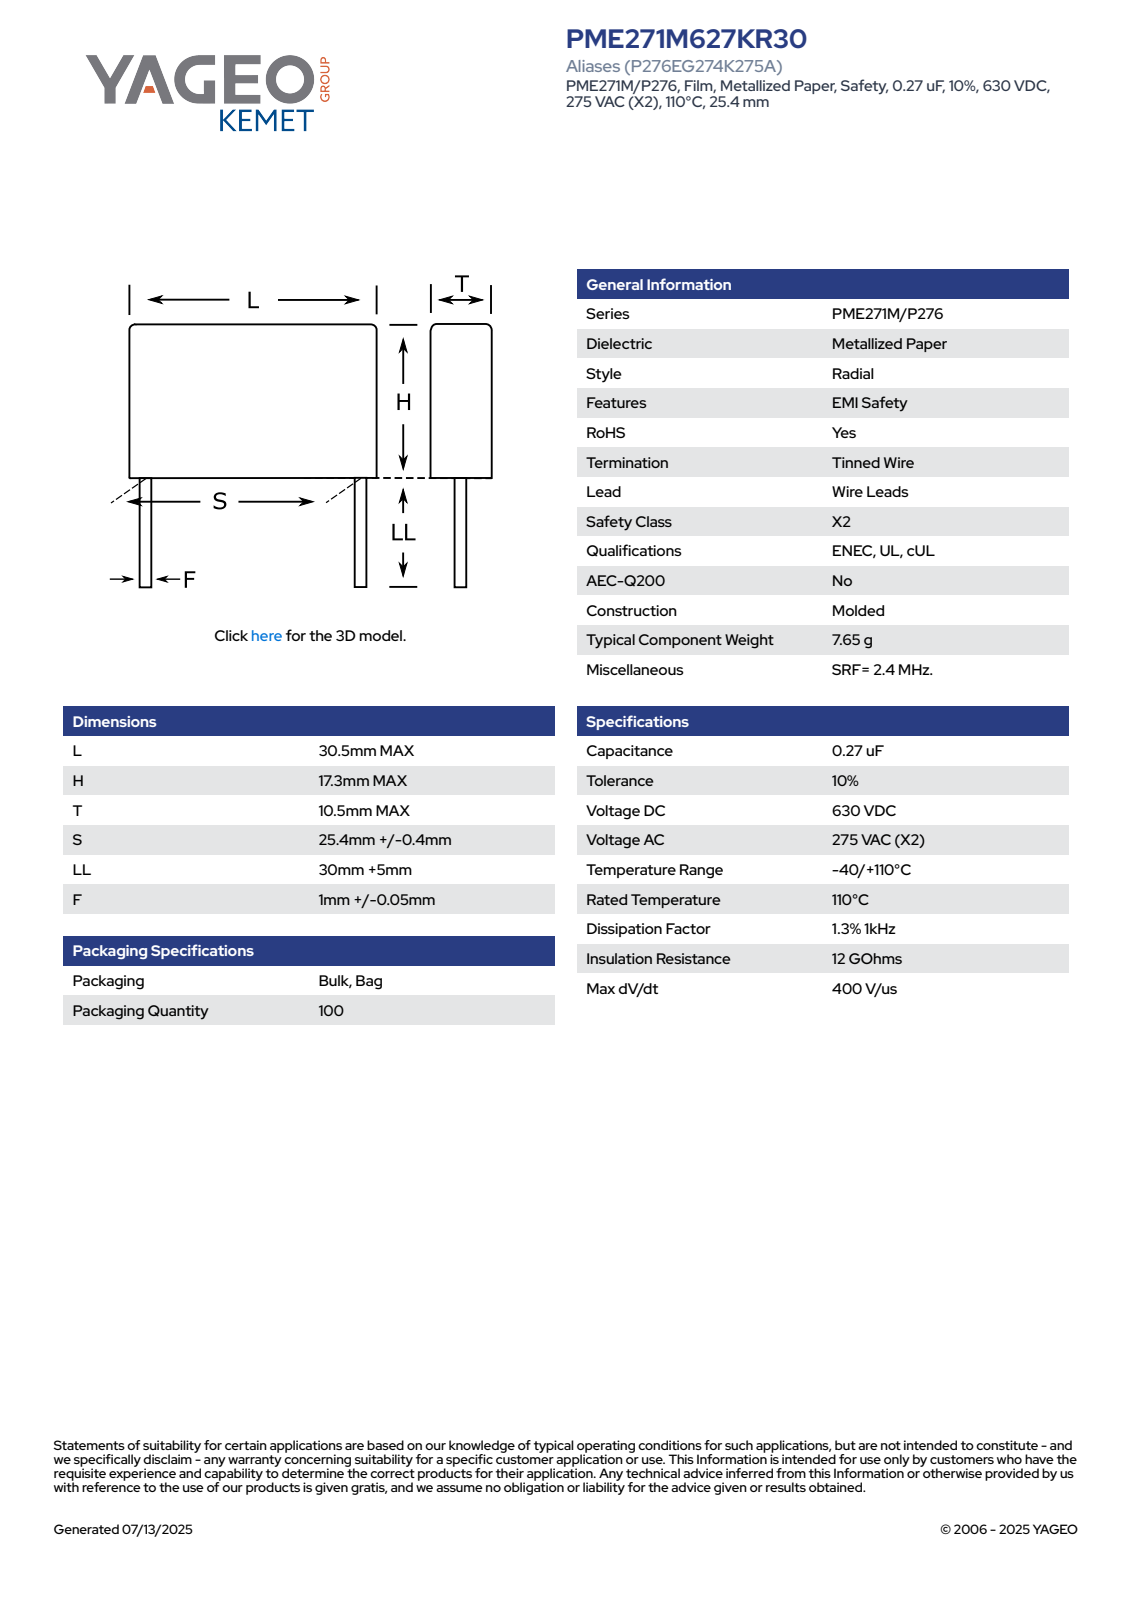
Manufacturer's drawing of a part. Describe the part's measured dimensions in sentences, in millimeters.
The part is named "CFR_MOLDED_30.5X17.3X10.5_L30.5H17.3T10.5S25.4LL35F1.05". Its 3-D file was written by "SolidWorks 2021 (AUTOMOTIVE_DESIGN)". It is 4 solids with 73 faces: 65 planar, 8 cylindrical and 0 other. Overall it measures 52.3 by 30.5 by 10.51 millimeters. Its volume is 5 597 cubic millimeters and its surface area 2 317 square millimeters. Round bosses or shafts: 2 of diameter 1.05. Partial cylindrical surfaces (rounded edges, fillets, slot ends): 4 of radius 0.5. The main face-to-face distances are 10.5, 17.3, 30.5, 10.51, 35, 52.3, 44.99, 9.99, 7.31, 42.25.
